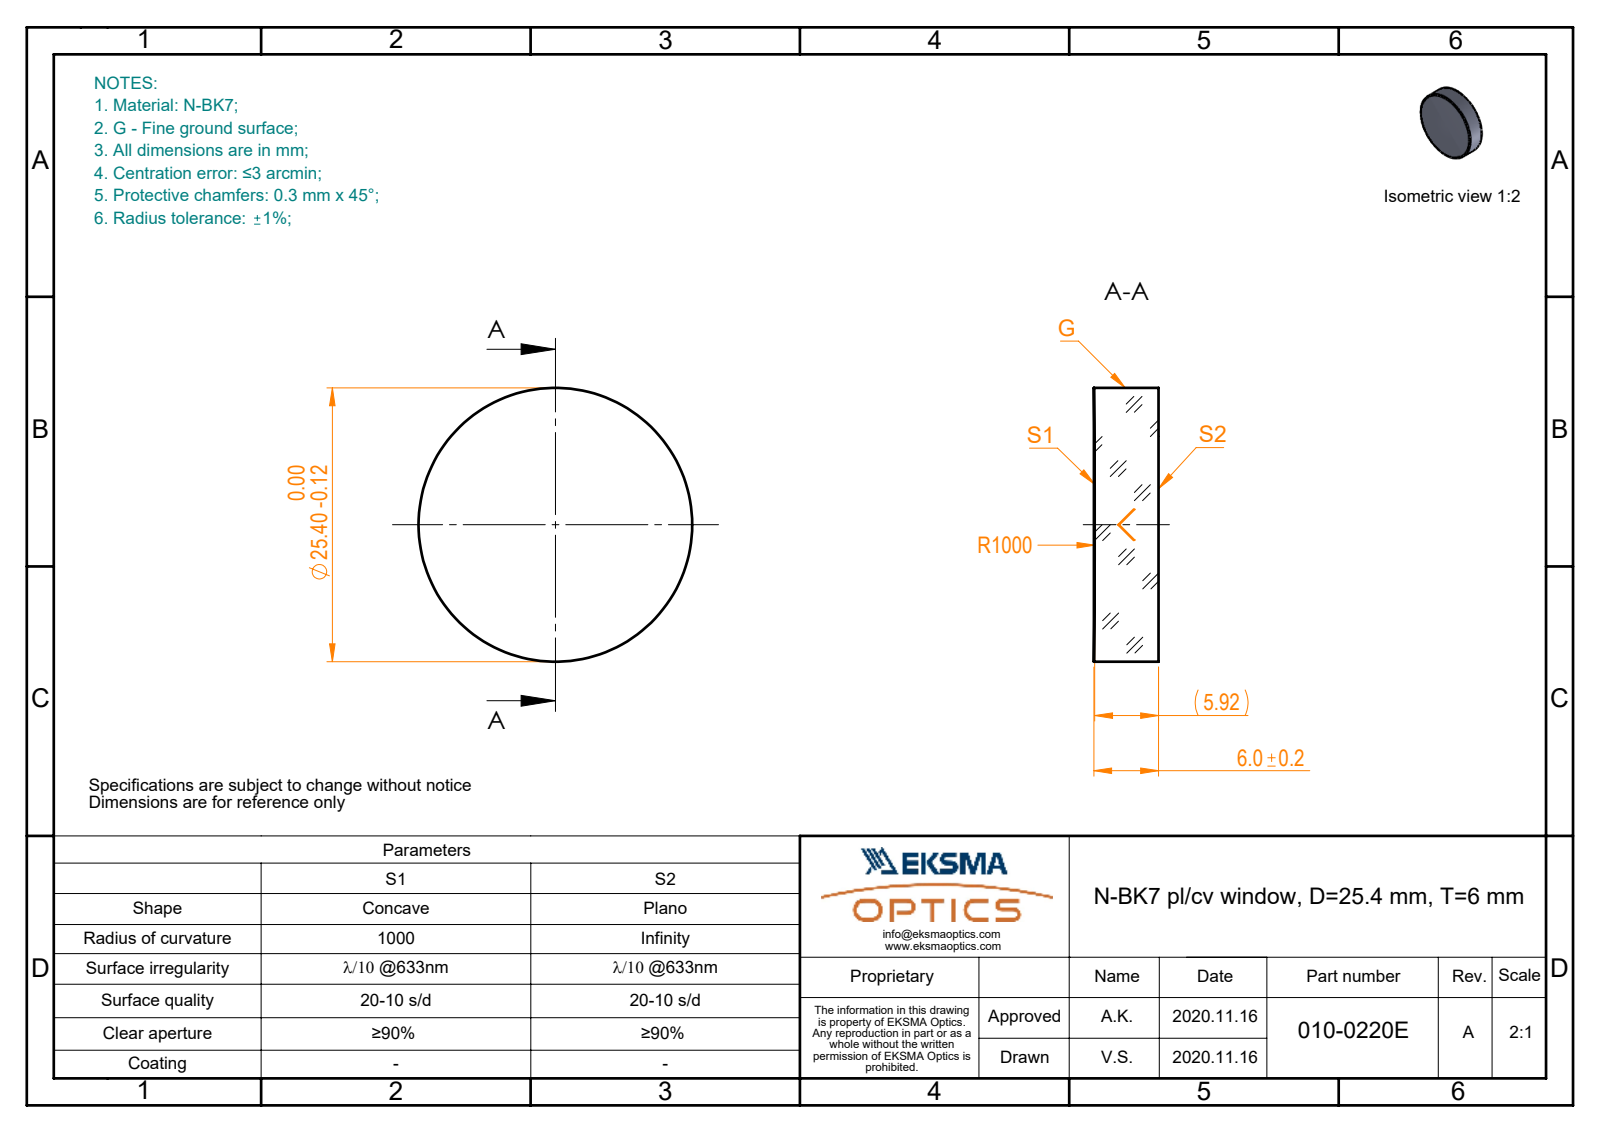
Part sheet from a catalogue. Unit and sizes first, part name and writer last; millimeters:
Units: millimetres
Overall size (bounding box): 25.4 × 25.4 × 6
Round bosses / shafts (diameter × count): ⌀25.4 ×1
Volume: 3 020 mm³ · Surface area: 1 492 mm²
Bodies: 1 solid, 5 faces (1 planar, 2 cylindrical, 2 other)
Part name (STEP PRODUCT): 010-0220E_N-BK7_PCV_window
STEP written by: SolidWorks 2019 (CONFIG_CONTROL_DESIGN)
